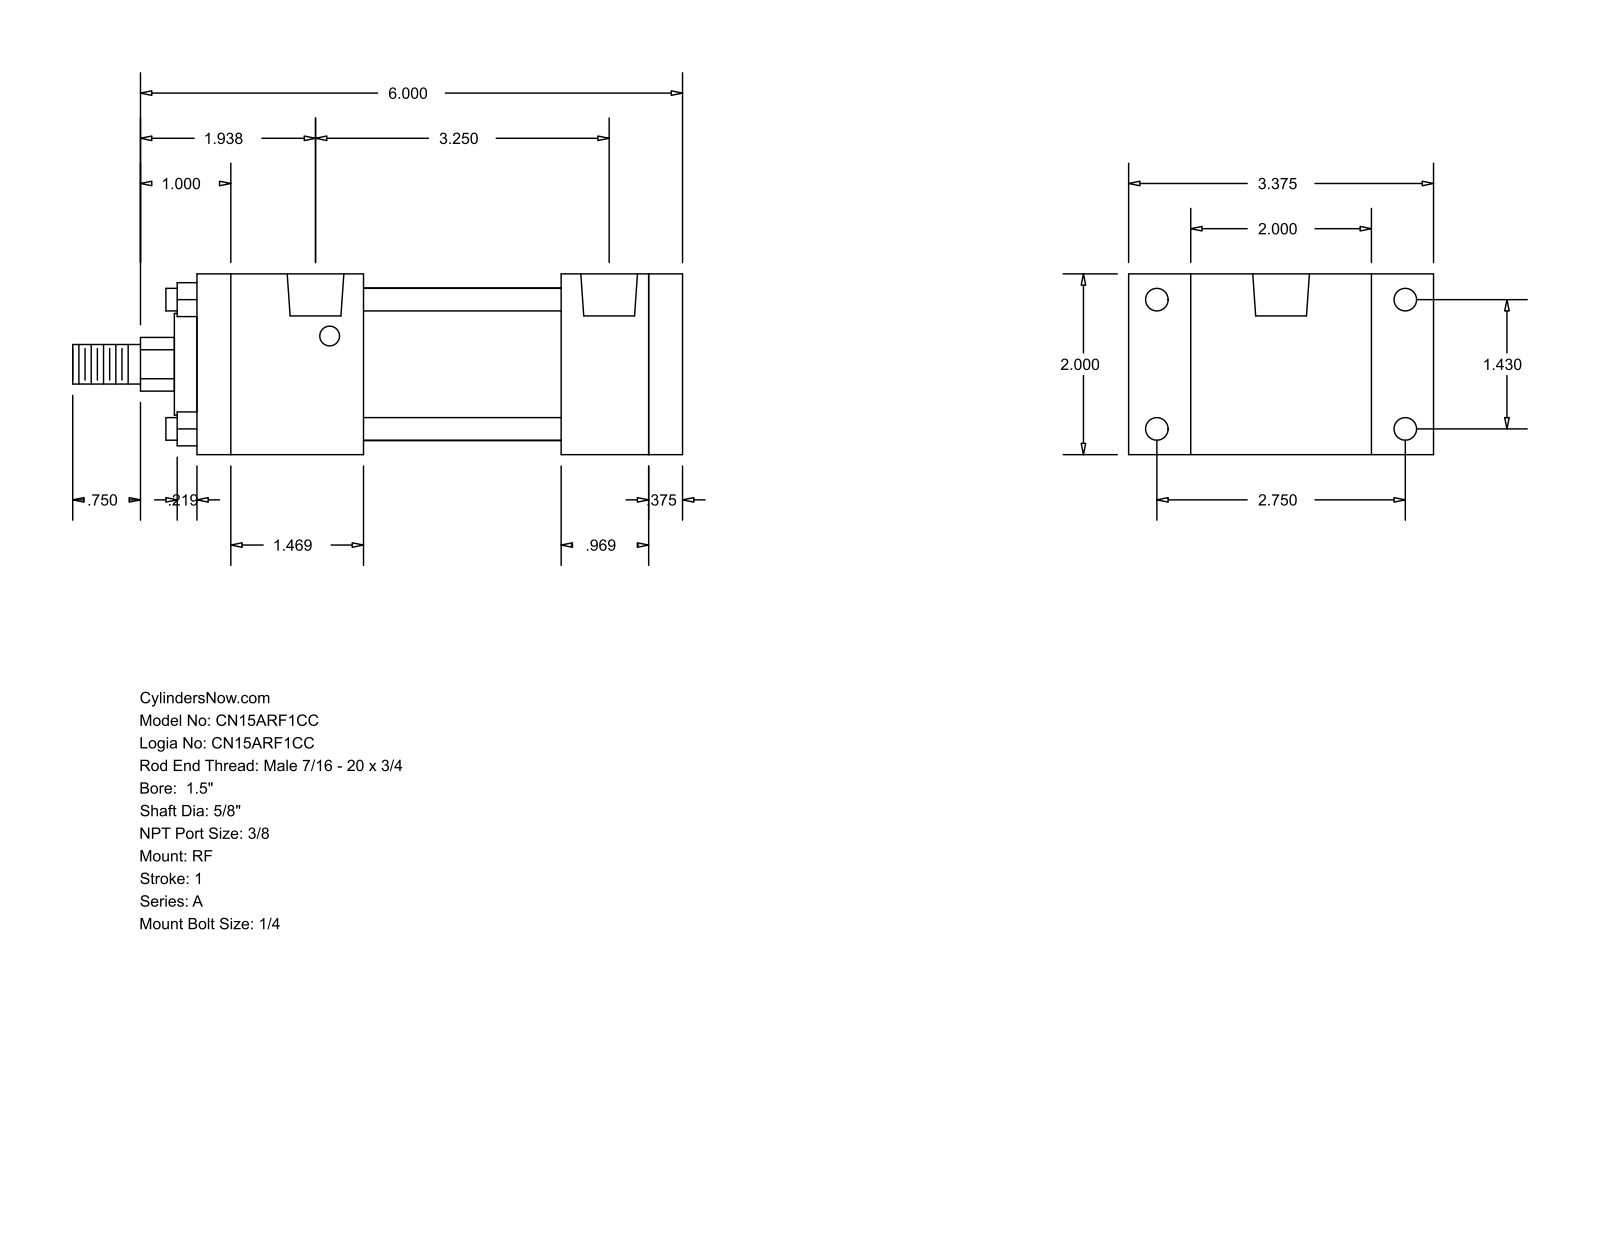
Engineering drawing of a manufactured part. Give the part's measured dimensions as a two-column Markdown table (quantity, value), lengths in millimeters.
| quantity | value |
| --- | --- |
| part name | A_RF__0150_0.625 |
| STEP written by | GSSL Pune (CONFIG_CONTROL_DESIGN) |
| units | millimeters |
| bodies | 0 solids, 92 faces (64 planar, 28 cylindrical, 0 other) |
| overall size | 171.45 × 85.72 × 50.8 |
| round holes (diameter × count) | 5.56 × 4, 6.35 × 4, 15.93 × 2 |
| round bosses / shafts (diameter × count) | 6.35 × 4, 42.93 × 1, 28.57 × 1, 15.88 × 1, 11.11 × 1 |
| partial cylindrical surfaces (radius × count) | 7.54 × 1 |
| main face-to-face distances | 50.8, 9.52, 127, 136.52, 102.39, 24.61, 34.13, 46.83, 55.56, 80.17 |
| hole center spacings | 3.97, 36.32, 69.84, 74.61, 78.58, 78.72, 82.55 |
